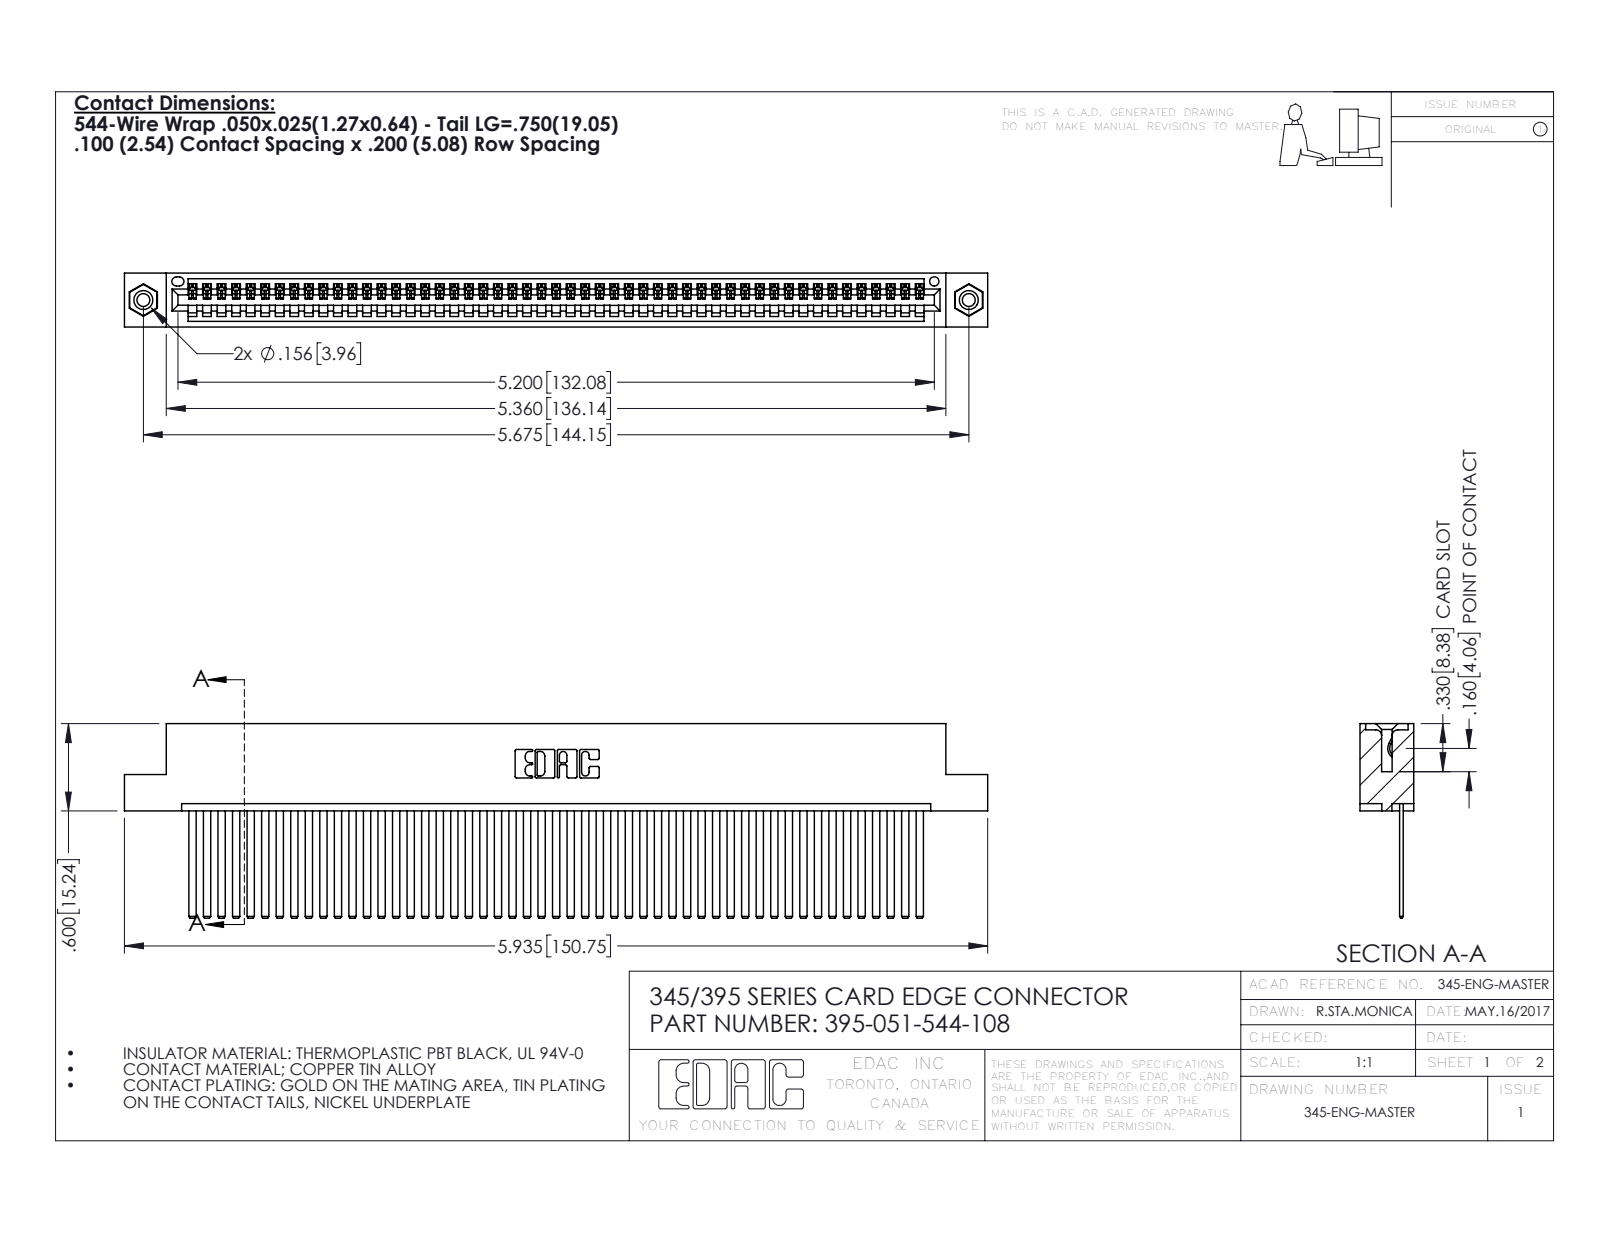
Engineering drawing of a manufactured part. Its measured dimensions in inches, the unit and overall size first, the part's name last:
Units: inches
Overall size (bounding box): 5.935 × 1.337 × 0.37
Round holes (diameter × count): ⌀0.089 ×2, ⌀0.125 ×2, ⌀0.156 ×2, ⌀0.064 ×1
Round bosses / shafts (diameter × count): ⌀0.155 ×2
Partial cylindrical surfaces — rounded edges, fillets, slot ends (radius × count): R0.006 ×102, R0.01 ×22, R0.007 ×6, R0.031 ×6, R0.026 ×3, R0.031 ×2, R0.04 ×2, R0.014 ×1
Main face-to-face distances: 0.072, 0.298, 0.025, 0.098, 0.272, 0.37, 0.2, 0.225, 0.149, 0.072
Hole centre spacings: 0.27, 5.439, 5.675
Volume: 0.914 in³ · Surface area: 33.82 in²
Bodies: 54 solids, 2838 faces (1948 planar, 874 cylindrical, 16 other)
Part name (STEP PRODUCT): 345 Part_Flush Mounting Lugs - 0.156 Dia-TI; 345-250-001_345-250-003-102; 345-292-001_345-293-144; 395-051-544-108
STEP written by: SolidWorks 2016 (CONFIG_CONTROL_DESIGN)
